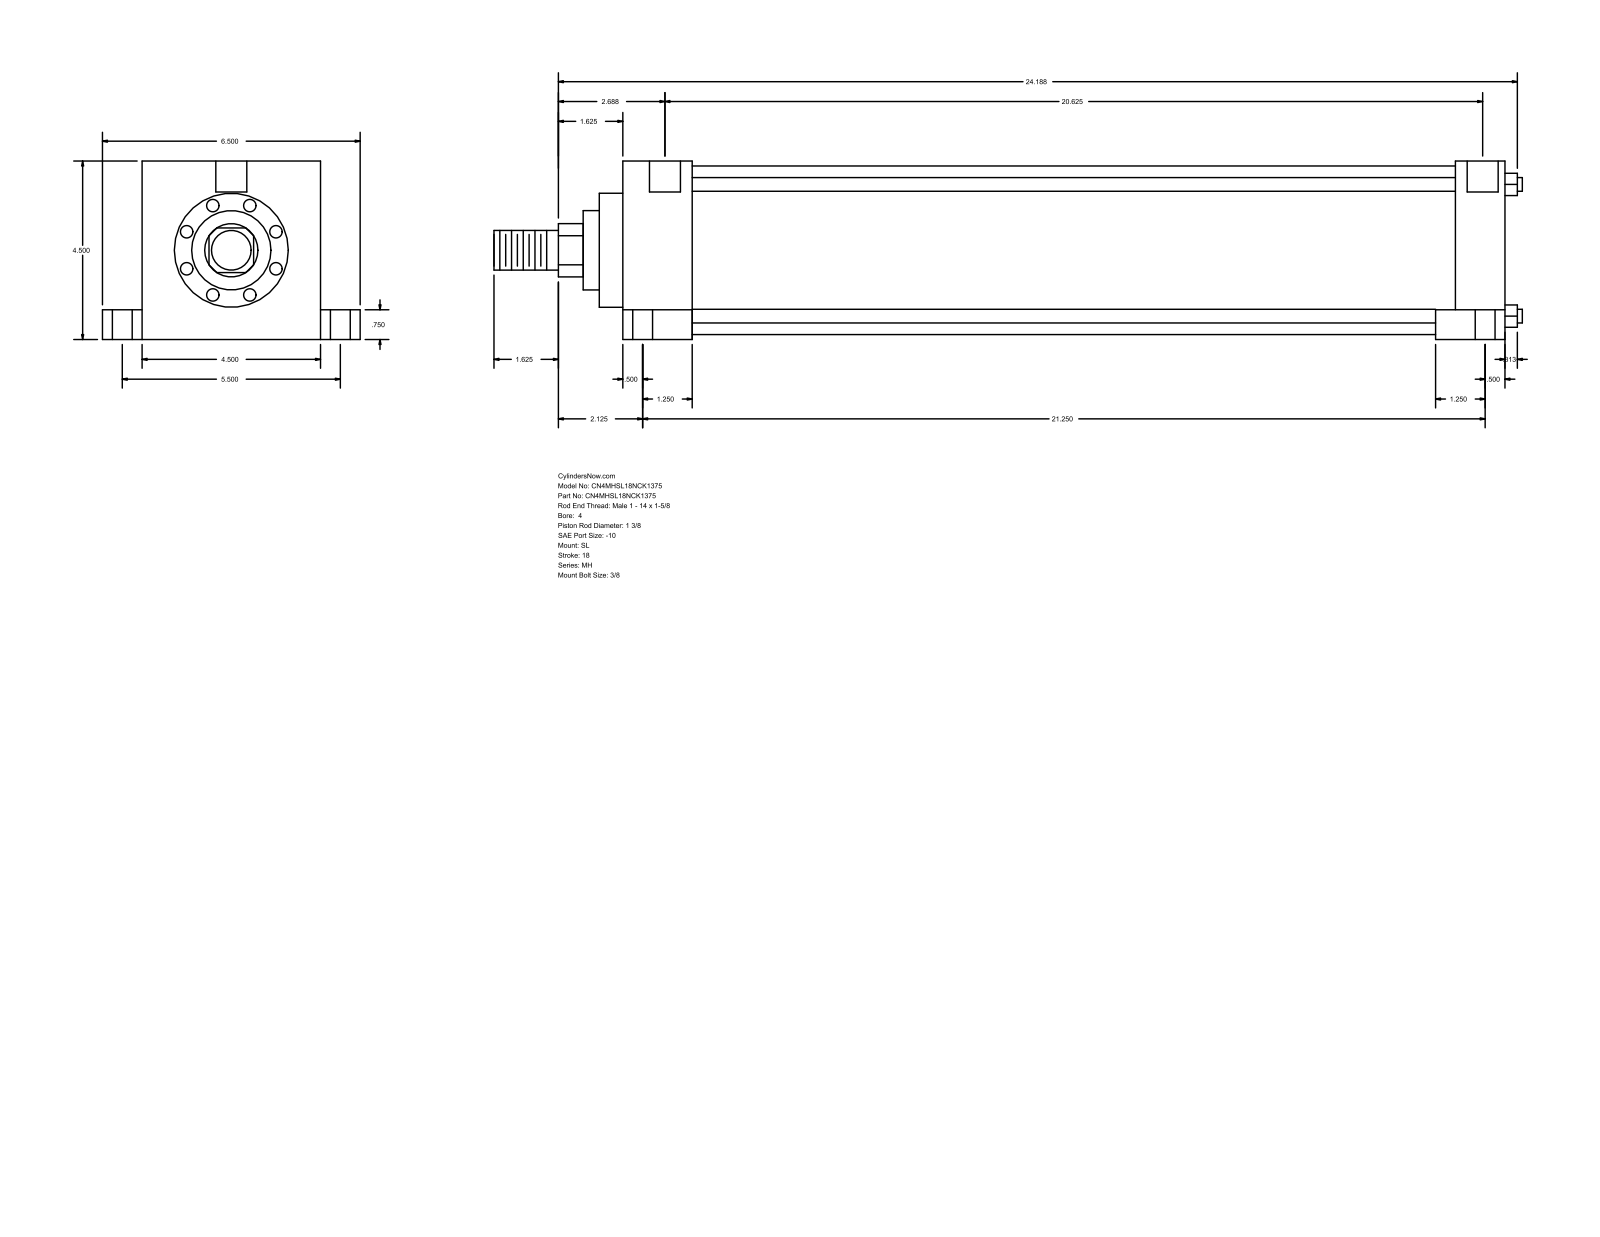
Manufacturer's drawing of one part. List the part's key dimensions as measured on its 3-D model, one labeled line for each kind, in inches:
Part name (STEP PRODUCT): MH_SL__0400_1.375
STEP written by: GSSL Pune (CONFIG_CONTROL_DESIGN)
Units: inches
Bodies: 0 solids, 110 faces (77 planar, 33 cylindrical, 0 other)
Overall size (bounding box): 25.937 × 6.5 × 4.5
Round holes (diameter × count): ⌀0.344 ×4, ⌀0.5 ×4, ⌀0.75 ×4, ⌀0.781 ×2
Round bosses / shafts (diameter × count): ⌀0.345 ×4, ⌀4.25 ×1, ⌀2.875 ×1, ⌀2 ×1, ⌀1.375 ×1, ⌀1 ×1
Partial cylindrical surfaces — rounded edges, fillets, slot ends (radius × count): R0.672 ×1
Main face-to-face distances: 4.5, 22.25, 1.75, 20.5, 21, 19.25, 1.25, 1, 5.5, 0.75
Hole centre spacings: 0.063, 2.75, 2.751, 2.795, 2.807, 5.5, 20.688, 20.75
